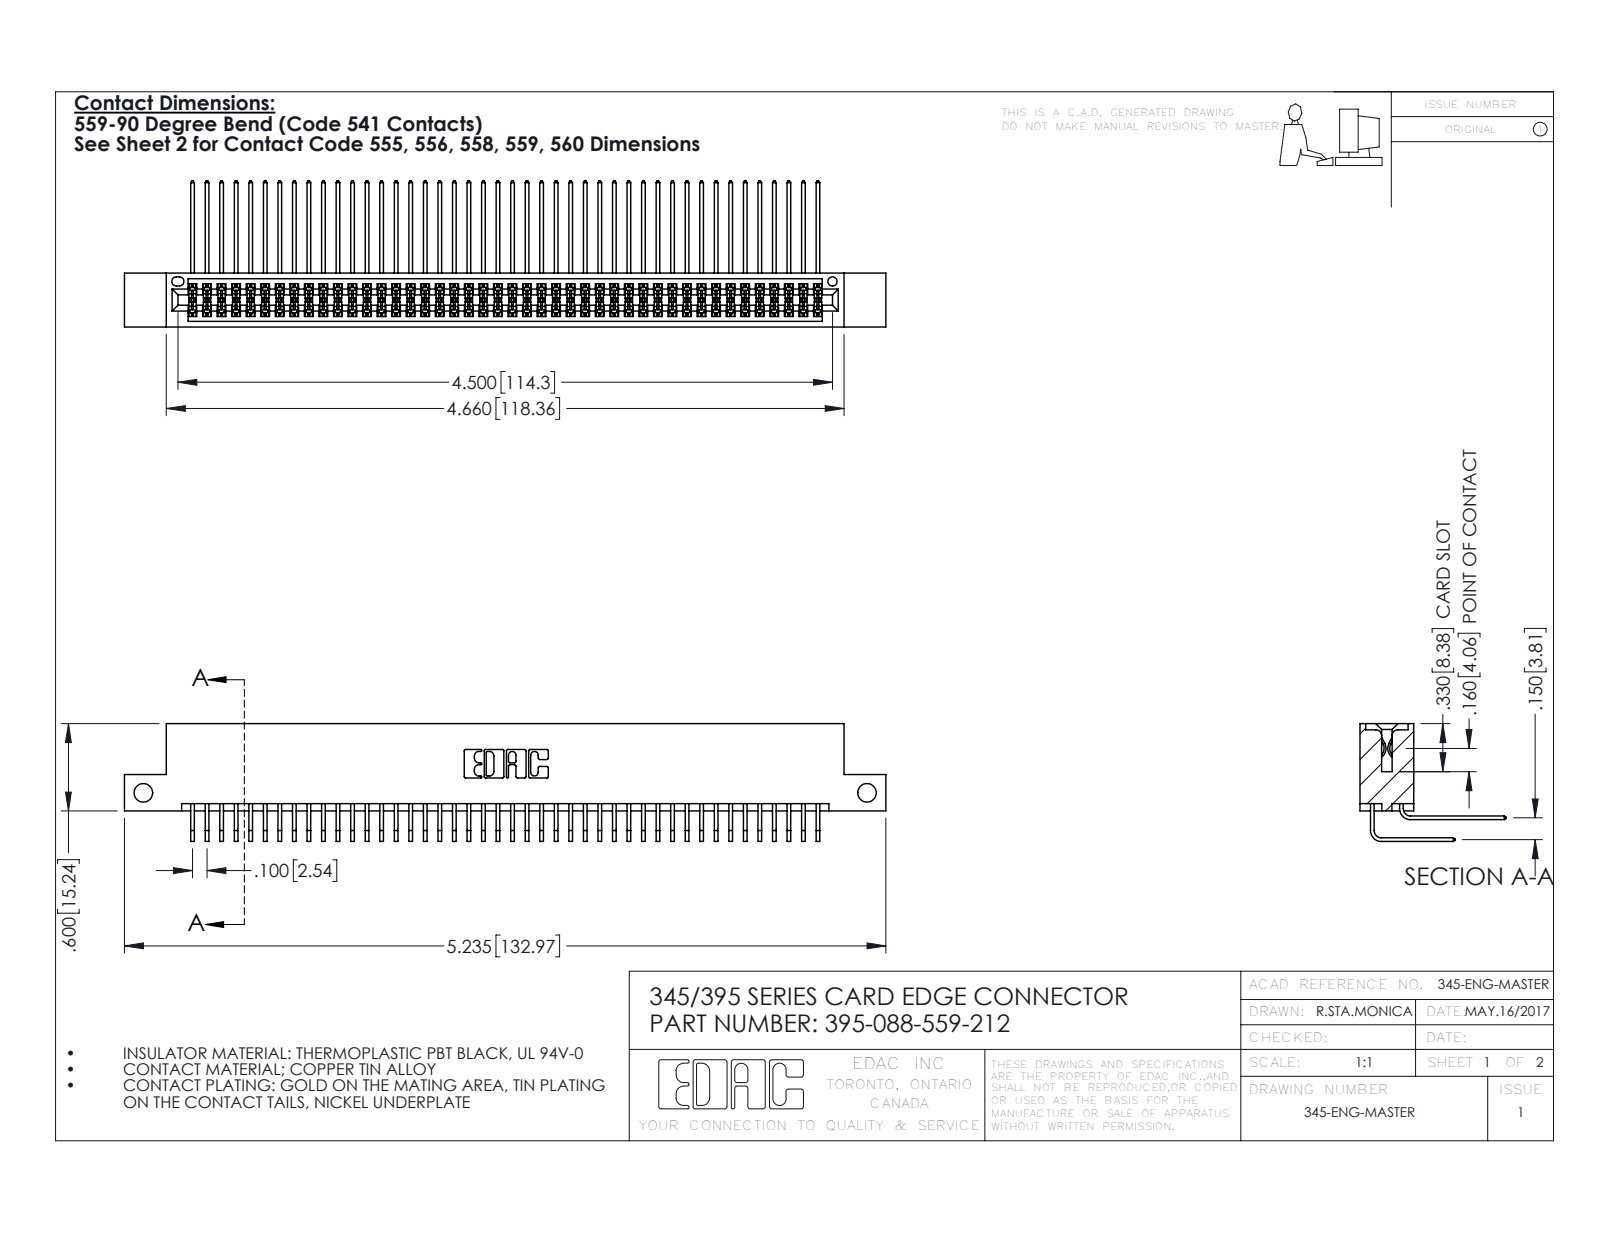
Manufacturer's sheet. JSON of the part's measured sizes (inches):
{"part_name": "345-292-001_559 Tail - 2; 345-292-001_558 559 Tail - 1; 345 Part_Flush Mounting Lugs - Side Mount; 395-088-559-212", "step_written_by": "SolidWorks 2016 (CONFIG_CONTROL_DESIGN)", "units": "inches", "bodies": {"solids": 89, "faces": 4702, "planar": 3160, "cylindrical": 1542, "other": 0}, "overall_size": [5.235, 1.005, 0.809], "volume_in3": 0.815, "surface_area_in2": 34.15, "round_holes": [[0.128, 2], [0.064, 1]], "partial_cylinders_radius": [[0.006, 133], [0.01, 22], [0.007, 6], [0.031, 6], [0.026, 3], [0.014, 2], [0.019, 2], [0.022, 2]], "face_to_face_distances": [0.072, 0.298, 0.2, 0.37, 0.098, 0.272, 0.025, 0.225, 0.175, 0.15], "hole_center_spacings": [4.975]}
